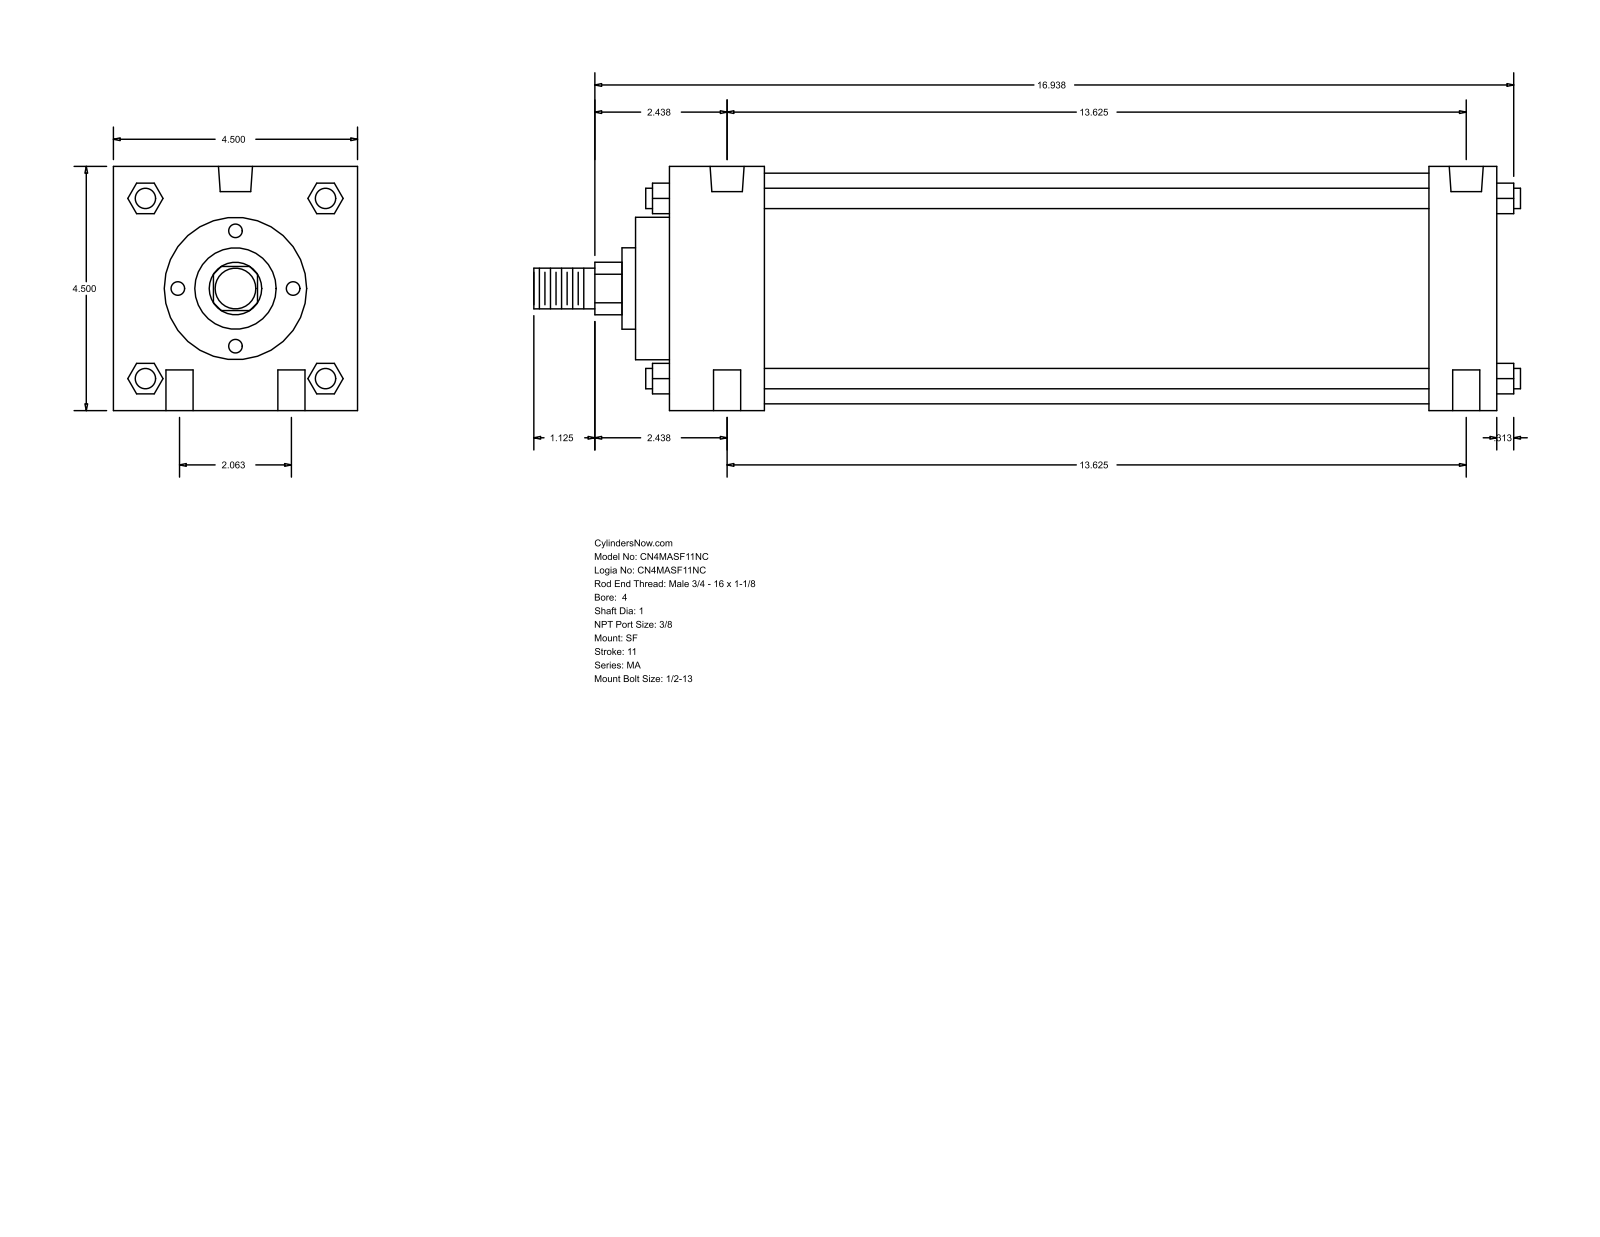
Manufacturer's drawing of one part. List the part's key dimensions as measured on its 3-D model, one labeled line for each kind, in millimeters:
Part name (STEP PRODUCT): MA_SF__0400_1
STEP written by: GSSL Pune (CONFIG_CONTROL_DESIGN)
Units: millimetres
Bodies: 0 solids, 126 faces (95 planar, 31 cylindrical, 0 other)
Overall size (bounding box): 461.96 × 114.3 × 114.3
Round holes (diameter × count): ⌀12.7 ×4, ⌀11.11 ×2, ⌀15.93 ×2
Round bosses / shafts (diameter × count): ⌀9.53 ×4, ⌀107.95 ×1, ⌀66.67 ×1, ⌀38.1 ×1, ⌀25.4 ×1, ⌀19.05 ×1
Partial cylindrical surfaces — rounded edges, fillets, slot ends (radius × count): R12.29 ×1
Main face-to-face distances: 114.3, 387.35, 355.6, 31.75, 44.46, 311.14, 342.89, 403.22, 15.87, 60.33
Hole centre spacings: 26.19, 347.07, 346.08, 52.38, 350.02, 336.56
